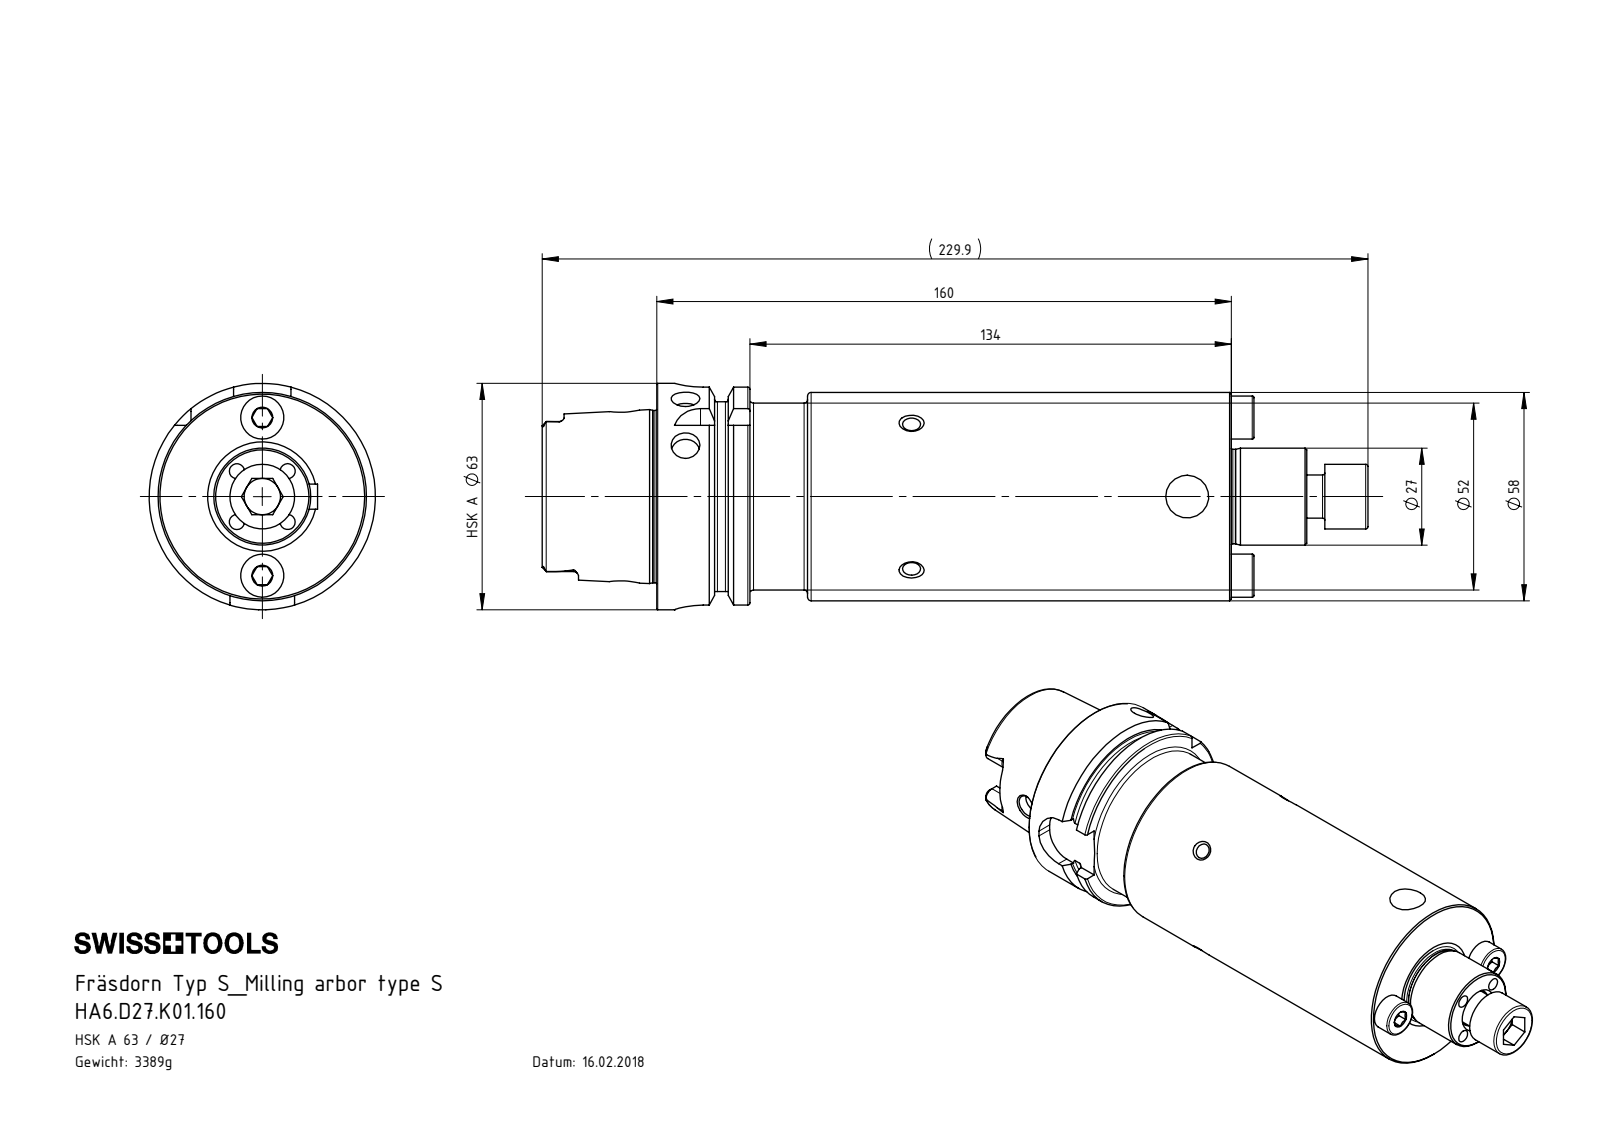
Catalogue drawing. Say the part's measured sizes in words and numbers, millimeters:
The part is named "HA6.D27.K01.160; D27-ER2.001.021_B; D27-ER1.002.030_A_Default; HA6-D27.K01.160_C_Fertigbearbeitung". Its 3-D file was written by "SolidWorks 2011 (AUTOMOTIVE_DESIGN)". It is 4 solids with 385 faces: 91 planar, 113 cylindrical and 181 other. Overall it measures 229.9 by 63 by 63 millimeters. Its volume is 431 805 cubic millimeters and its surface area 60 581 square millimeters. Round holes: 6 of diameter 5, 3 of diameter 4.2, 3 of diameter 10, 2 of diameter 8, 1 of diameter 7.5, 1 of diameter 8.4, 1 of diameter 10.25, 1 of diameter 13, 1 of diameter 17, 1 of diameter 19, 1 of diameter 34, 1 of diameter 40. Round bosses or shafts: 3 of diameter 12, 2 of diameter 6, 2 of diameter 4.6, 1 of diameter 63, 1 of diameter 58, 1 of diameter 54.95, 1 of diameter 52, 1 of diameter 47.94. Partial cylindrical surfaces (rounded edges, fillets, slot ends): 6 of radius 1.4, 4 of radius 2.88, 4 of radius 8, 2 of radius 3.5. The main face-to-face distances are 160, 16, 25.95, 134.05, 9.95, 150.05, 21, 31.9, 41.85, 57.85. The hole center spacings are 10, 16.52, 22, 29.92, 79.05, 20, 44.
